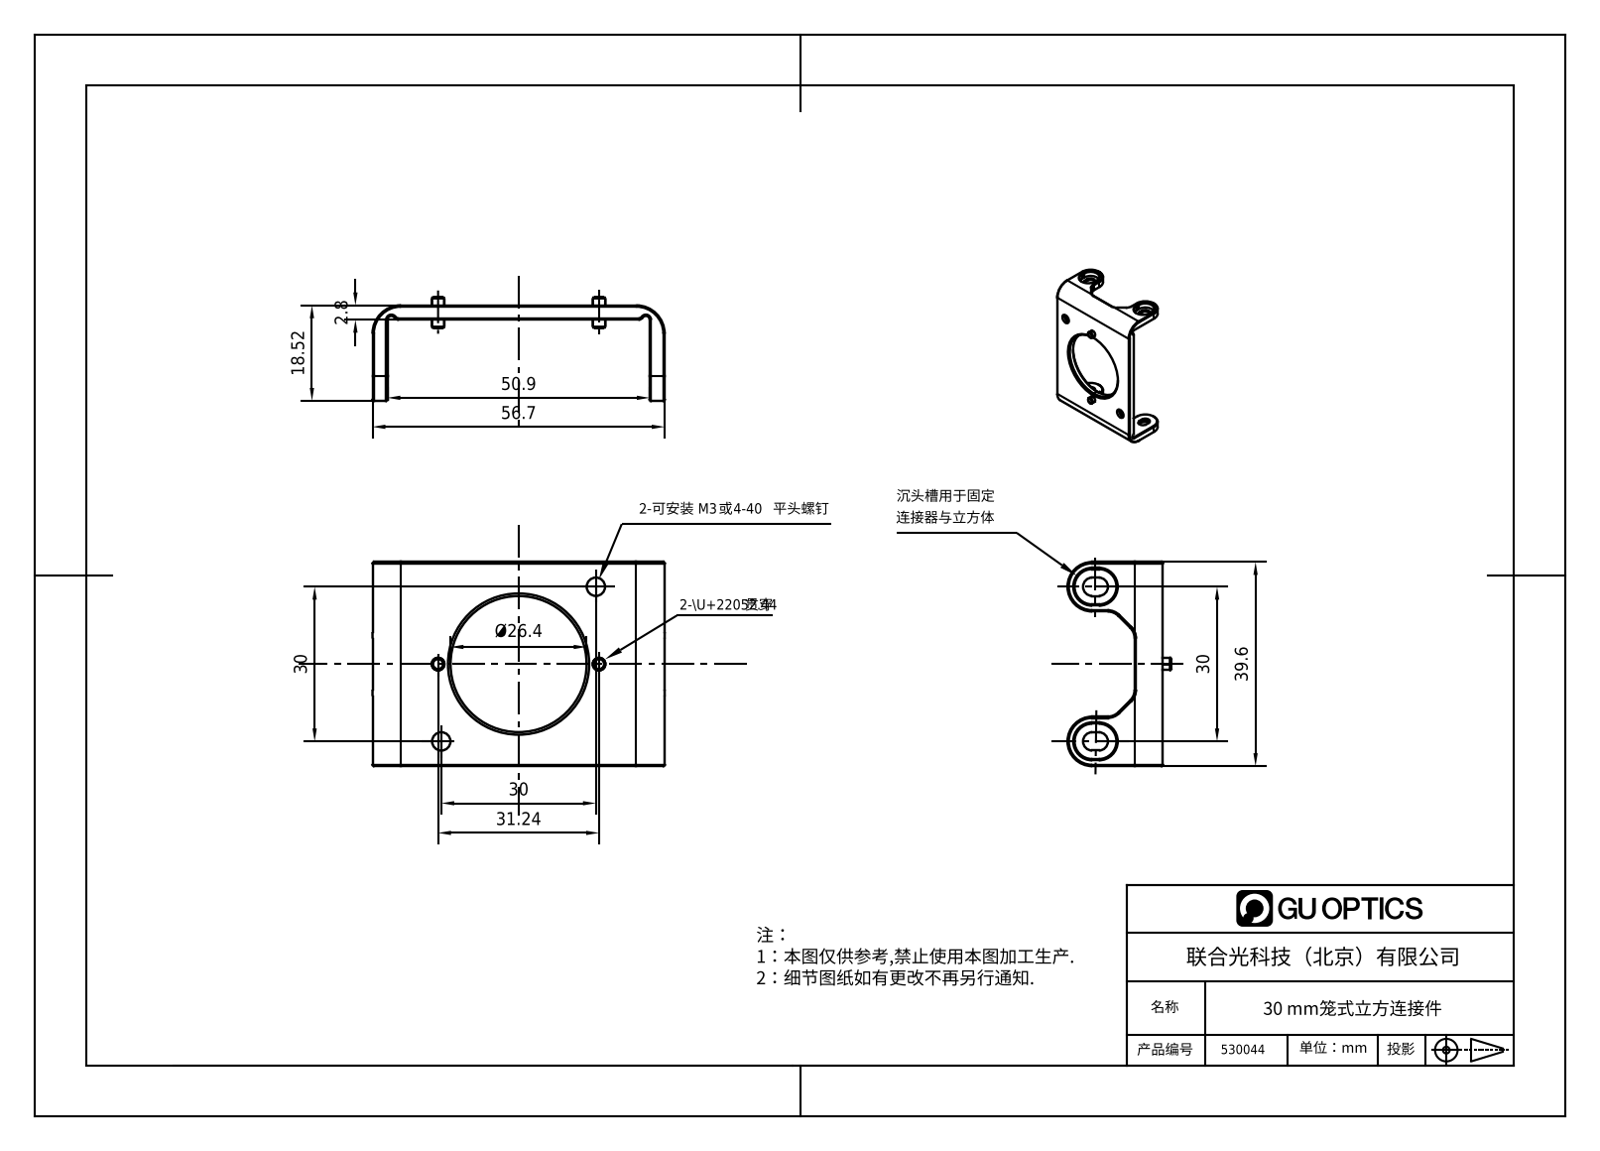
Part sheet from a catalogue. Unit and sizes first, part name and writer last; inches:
Units: inches
Overall size (bounding box): 2.232 × 1.559 × 0.792
Round holes (diameter × count): ⌀0.14 ×2, ⌀0.265 ×2, ⌀1.039 ×1
Round bosses / shafts (diameter × count): ⌀0.094 ×2
Partial cylindrical surfaces — rounded edges, fillets, slot ends (radius × count): R0.07 ×4, R0.118 ×4, R0.135 ×4, R0.03 ×2, R0.039 ×2, R0.189 ×2, R0.217 ×2
Main face-to-face distances: 0.11, 2.004, 0.114, 2.118, 1.559, 2.232, 0.085, 2.147, 0.029, 2.033
Hole centre spacings: 0.835, 1.67
Bodies: 0 solids, 198 faces (86 planar, 48 cylindrical, 64 other)
Part name (STEP PRODUCT): 2.2.7.5_L30F-BL_30 mm笼式立方连接件
STEP written by: SolidWorks 2018 (AUTOMOTIVE_DESIGN)
